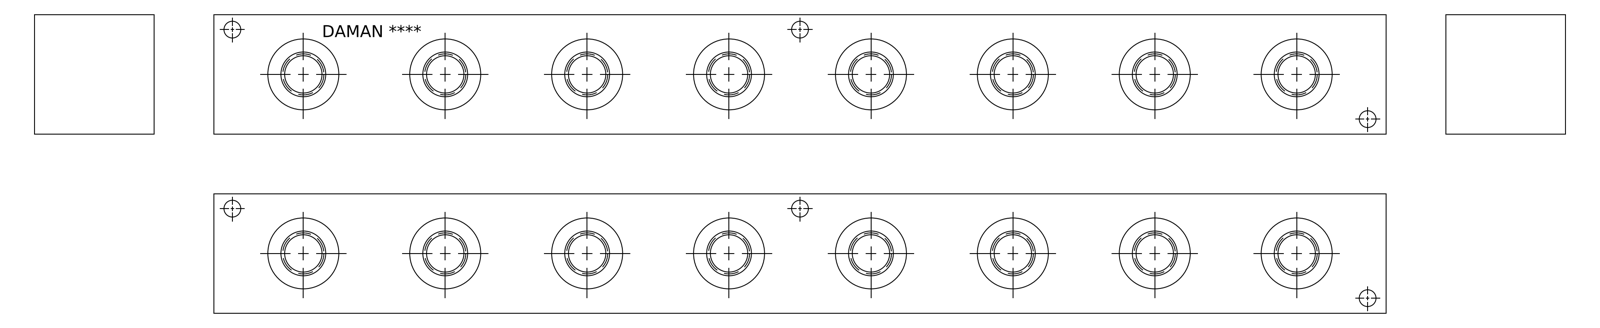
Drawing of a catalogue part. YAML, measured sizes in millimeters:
part_name: "Part_AJ0900808S_3D"
step_written_by: "Autodesk Inventor 2019 (AUTOMOTIVE_DESIGN)"
units: millimeters
bodies: {solids: 1, faces: 517, planar: 227, cylindrical: 92, other: 198}
overall_size: [498.48, 50.8, 50.8]
volume: 1171000
surface_area: 130752
round_holes:
  - {diameter: 15.88, count: 16}
  - {diameter: 17.5, count: 16}
  - {diameter: 19.05, count: 16}
  - {diameter: 19.25, count: 16}
  - {diameter: 30.63, count: 16}
  - {diameter: 7.14, count: 6}
face_to_face_distances: [50.8, 50.01, 0.79, 498.48, 35.74, 14.27, 15.06, 1, 49.8, 14.06]
hole_center_spacings: [120.65, 60.33, 180.98, 60.32, 241.3, 301.63, 35.66, 35.69]
